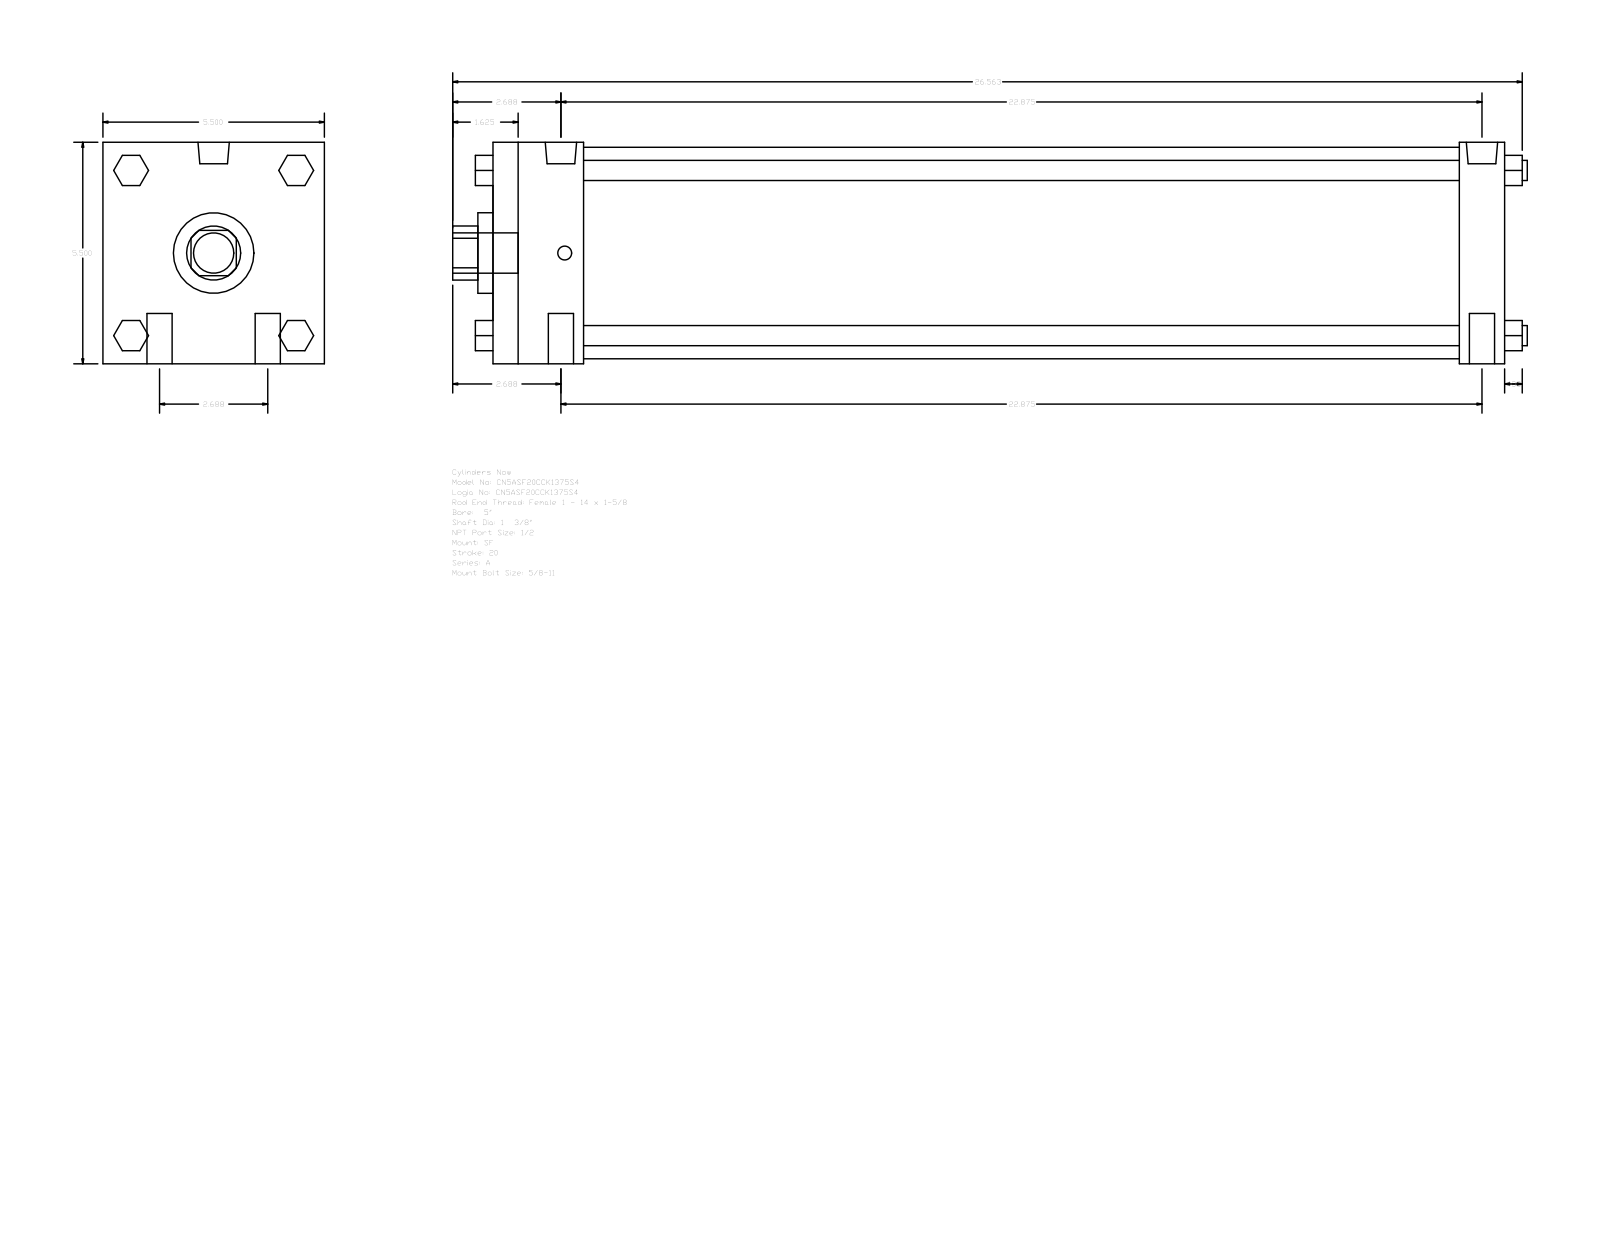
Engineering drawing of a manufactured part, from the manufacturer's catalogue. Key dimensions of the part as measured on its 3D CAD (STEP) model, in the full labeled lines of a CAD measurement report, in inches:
Part name (STEP PRODUCT): A_SF__0500_1.375
STEP written by: GSSL Pune (CONFIG_CONTROL_DESIGN)
Units: inches
Bodies: 0 solids, 124 faces (94 planar, 30 cylindrical, 0 other)
Overall size (bounding box): 26.687 × 5.5 × 5.5
Round holes (diameter × count): ⌀1.375 ×1, ⌀2 ×1, ⌀5.25 ×1
Round bosses / shafts (diameter × count): ⌀0.625 ×4, ⌀0.5 ×4, ⌀0.778 ×2, ⌀0.344 ×2, ⌀1 ×1
Partial cylindrical surfaces — rounded edges, fillets, slot ends (radius × count): R0.672 ×1
Main face-to-face distances: 5.5, 25.125, 1.125, 2.25, 24, 21.75, 22.875, 0.75, 2.05, 3.55
